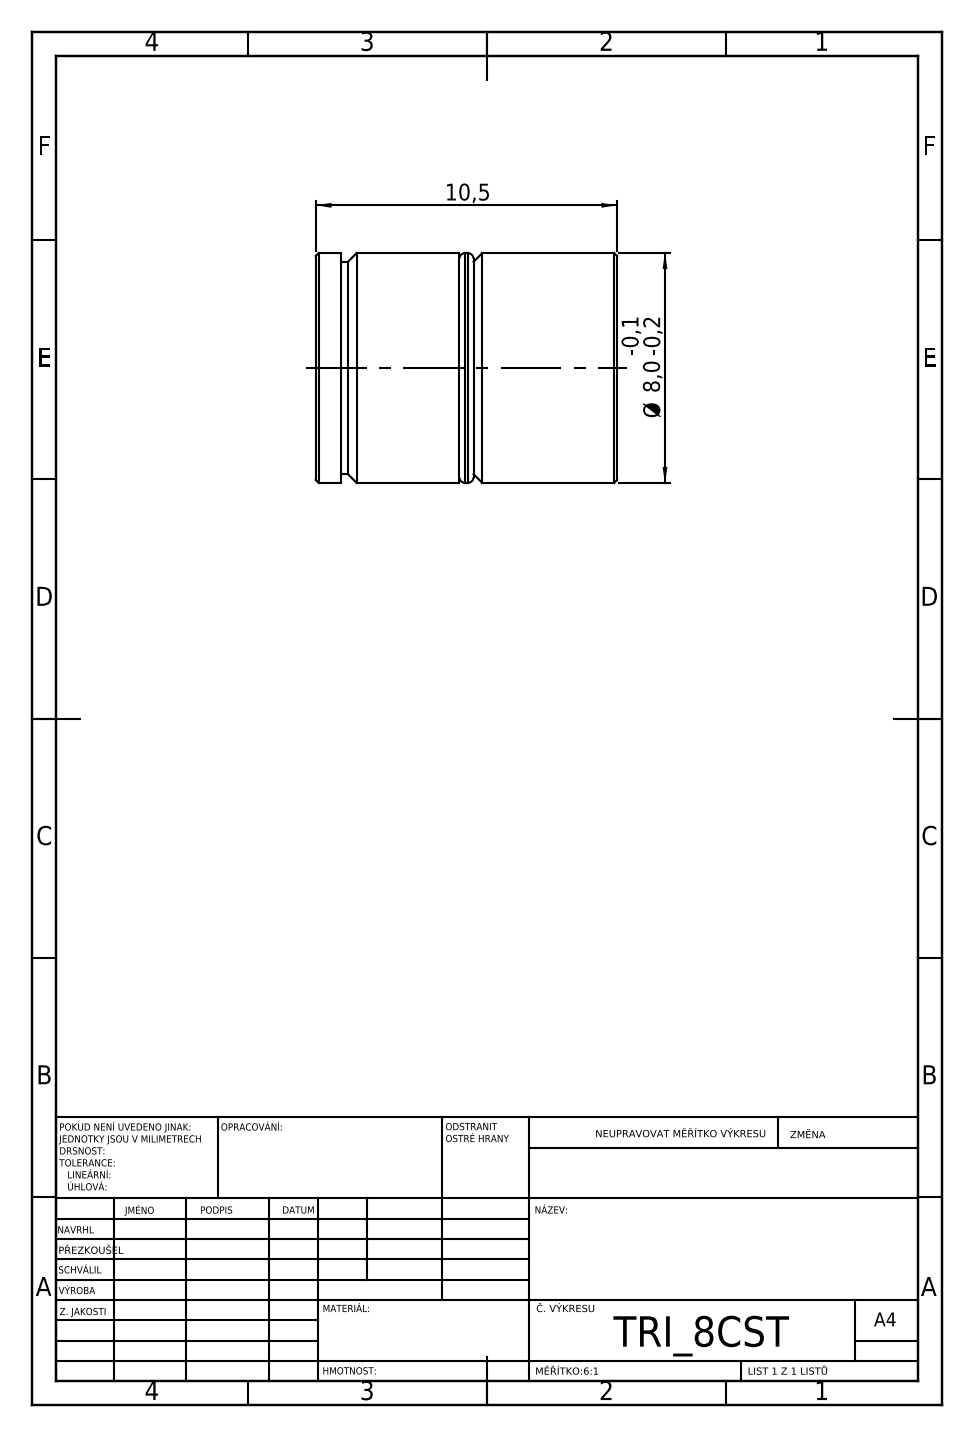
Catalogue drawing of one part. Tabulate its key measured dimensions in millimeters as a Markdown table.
| quantity | value |
| --- | --- |
| STEP written by | SolidWorks 2019 (CONFIG_CONTROL_DESIGN) |
| units | millimeters |
| bodies | 2 solids, 43 faces (19 planar, 12 cylindrical, 12 other) |
| overall size | 10.5 × 8 × 8 |
| volume | 511 mm³ |
| surface area | 508 mm² |
| round bosses / shafts (diameter × count) | 8 × 1, 7.4 × 1 |
| main face-to-face distances | 5, 5.5, 0.5, 4, 4.5, 9.5, 1, 10.5, 6.2, 9.63 |
